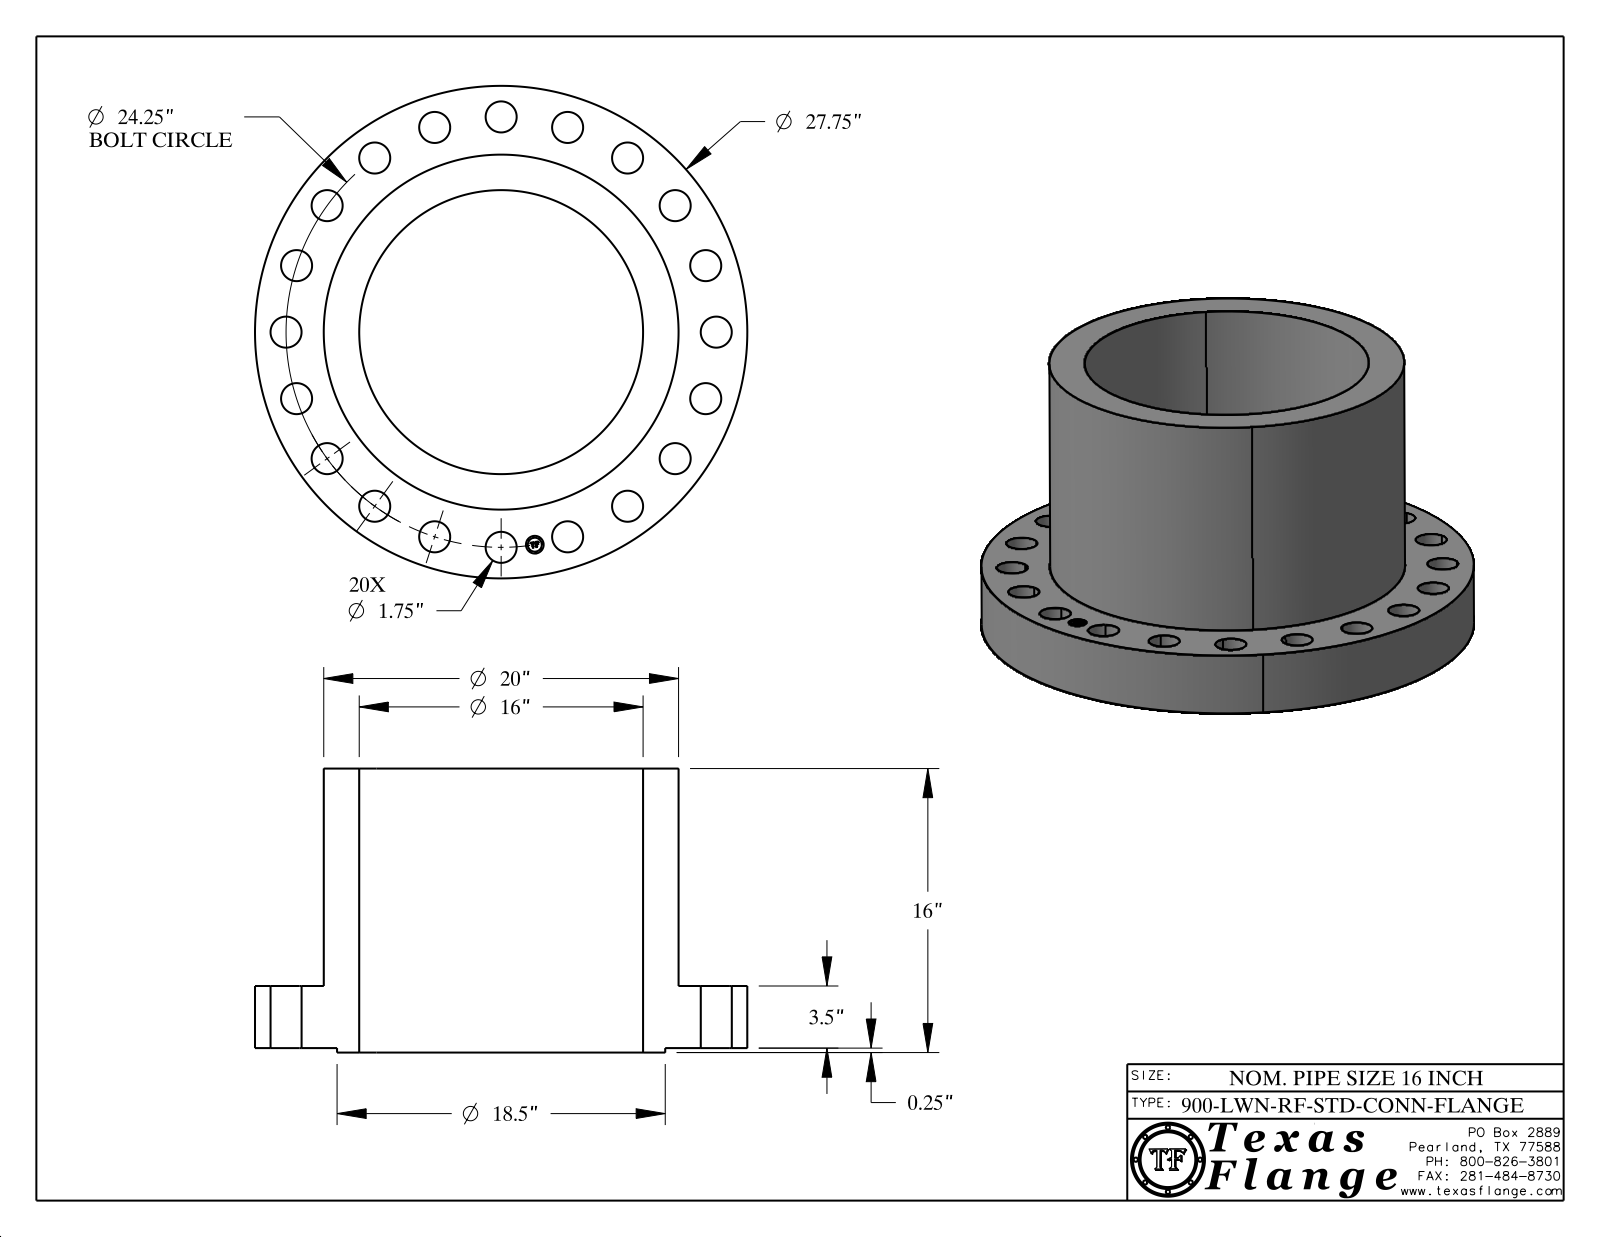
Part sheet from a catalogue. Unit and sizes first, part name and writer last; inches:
Units: inches
Overall size (bounding box): 27.75 × 27.75 × 16
Round holes (diameter × count): ⌀1.75 ×20, ⌀1 ×1, ⌀16 ×1
Round bosses / shafts (diameter × count): ⌀0.061 ×8, ⌀27.75 ×1, ⌀20 ×1, ⌀18.5 ×1, ⌀0.788 ×1
Main face-to-face distances: 3.5, 15.75, 12.25, 0.25, 3.75, 16, 3.745, 3.495, 12.255, 0.298
Hole centre spacings: 17.147, 23.063, 19.619, 12.125, 3.794, 7.494, 11.009, 14.254
Volume: 2 647 in³ · Surface area: 2 990 in²
Bodies: 1 solid, 437 faces (369 planar, 68 cylindrical, 0 other)
Part name (STEP PRODUCT): 16-900-LWN-RF-STD-CONN-FLANGE
STEP written by: CATIA V5 STEP AP214 (AUTOMOTIVE_DESIGN)
